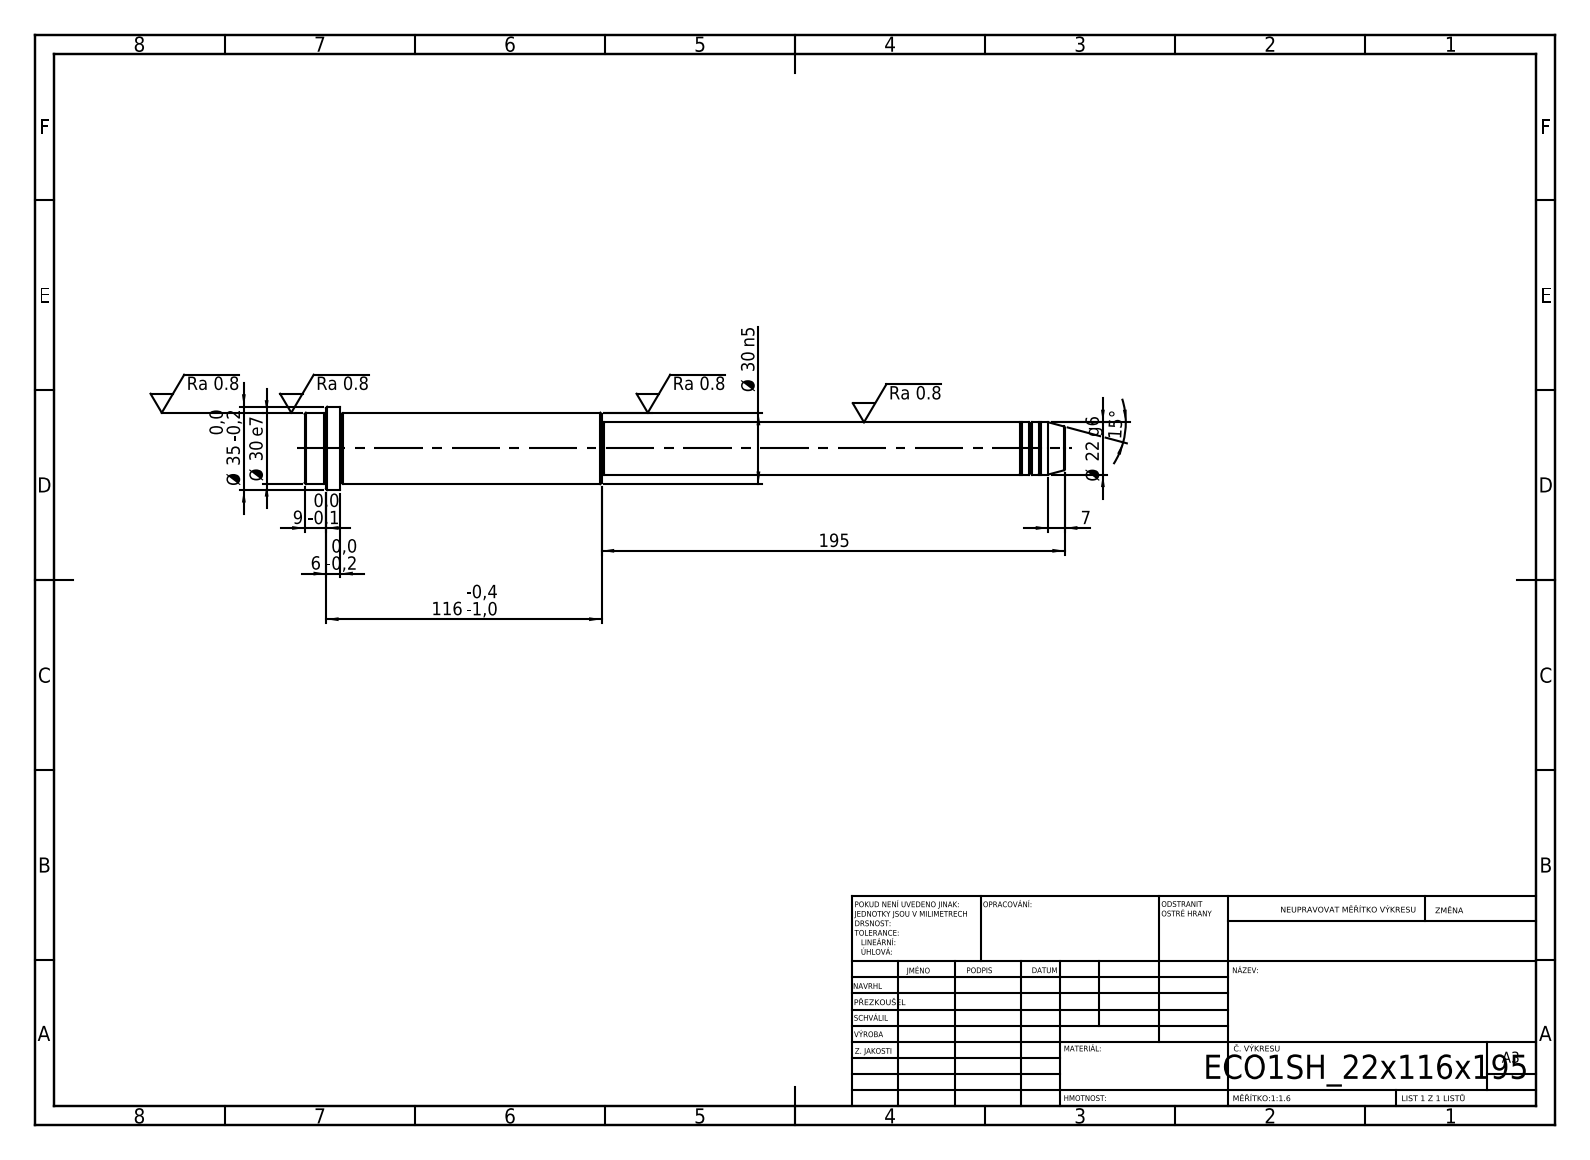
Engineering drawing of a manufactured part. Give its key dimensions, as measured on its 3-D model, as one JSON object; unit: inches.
{"step_written_by": "SolidWorks 2019 (CONFIG_CONTROL_DESIGN)", "units": "inches", "bodies": {"solids": 1, "faces": 52, "planar": 6, "cylindrical": 16, "other": 30}, "overall_size": [12.598, 1.378, 1.378], "volume_in3": 9.969, "surface_area_in2": 42.33, "round_bosses_or_shafts": [[1.378, 1], [1.181, 1], [0.866, 1], [0.827, 1]], "face_to_face_distances": [4.921, 4.331, 0.591, 7.677, 12.008, 12.598, 12.244, 4.567, 0.236, 0.354]}
